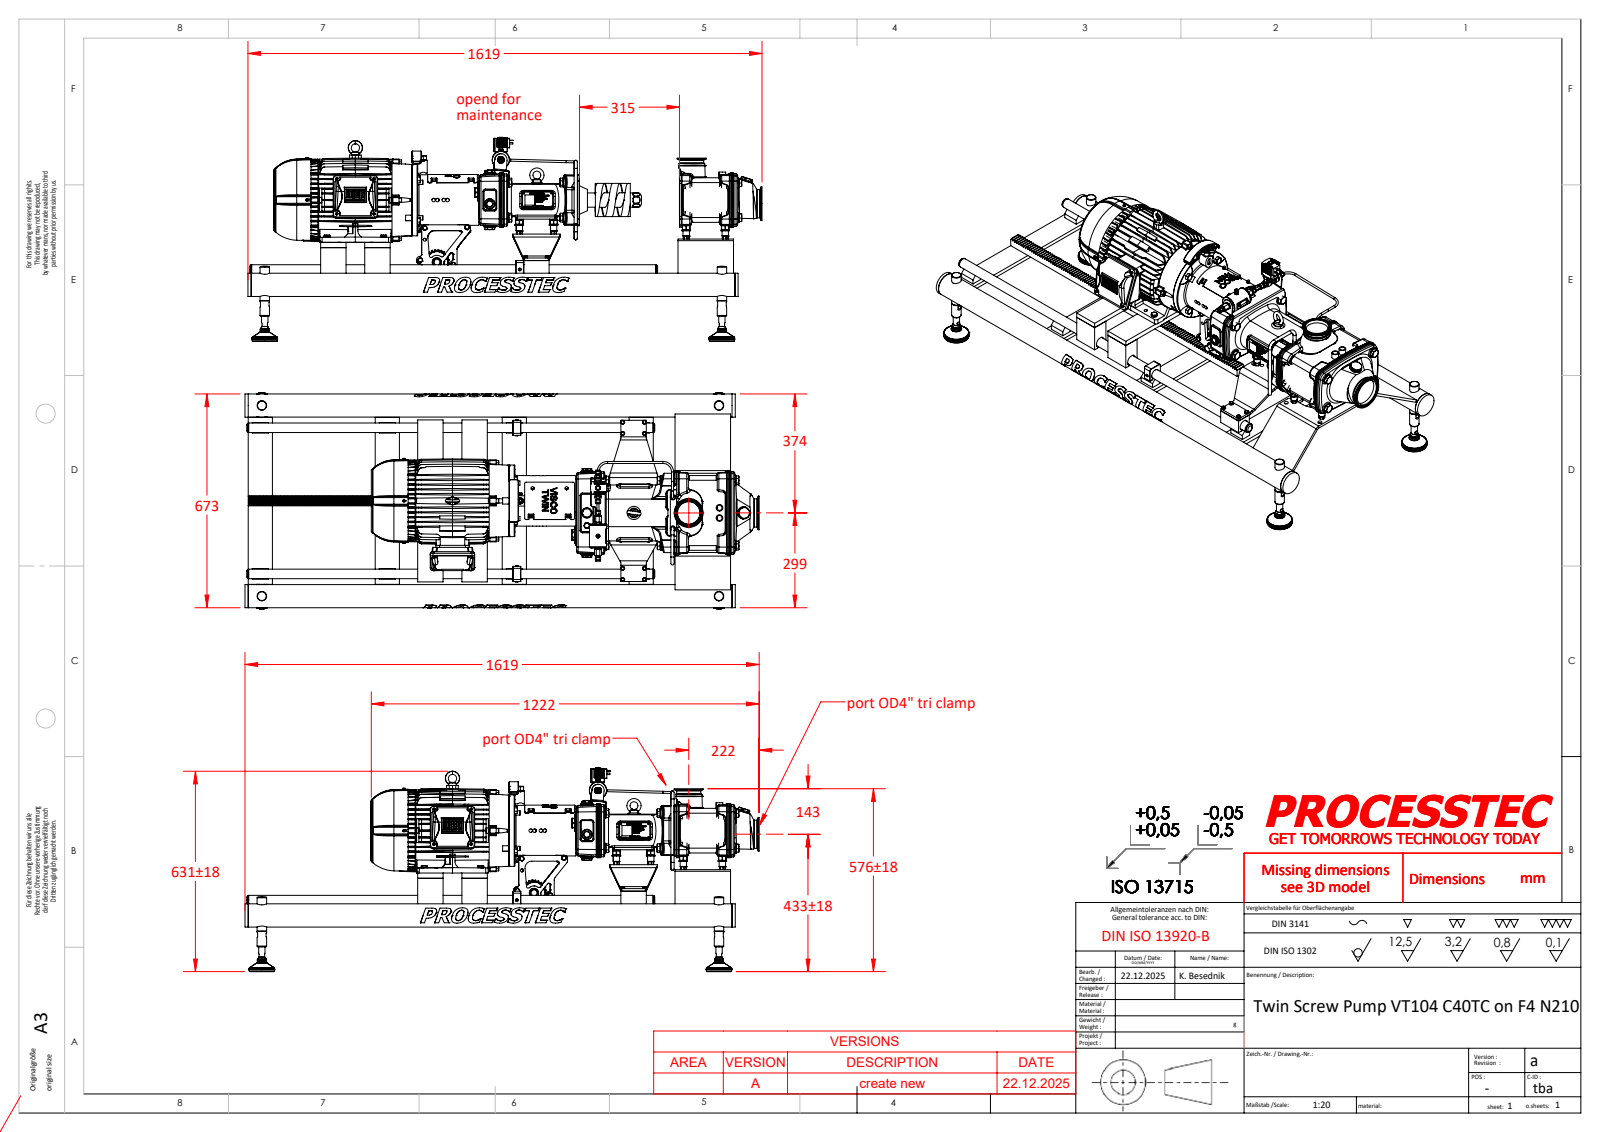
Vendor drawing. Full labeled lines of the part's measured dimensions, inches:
Part name (STEP PRODUCT): 001482; 001076; 001406; 000369 (+8 more)
STEP written by: SolidWorks 2023 (AUTOMOTIVE_DESIGN)
Units: inches
Bodies: 195 solids, 20316 faces (8834 planar, 4079 cylindrical, 7403 other)
Overall size (bounding box): 63.76 × 26.791 × 25.257
Volume: 3 233 in³ · Surface area: 10 180 in²
Round holes (diameter × count): ⌀0.335 ×22, ⌀0.197 ×21, ⌀0.315 ×13, ⌀0.433 ×12, ⌀0.512 ×12, ⌀0.268 ×11, ⌀0.252 ×10, ⌀0.413 ×9, ⌀0.689 ×9, ⌀0.398 ×8, ⌀0.402 ×8, ⌀0.404 ×8
Round bosses / shafts (diameter × count): ⌀0.394 ×38, ⌀0.236 ×22, ⌀0.945 ×20, ⌀0.669 ×16, ⌀0.787 ×12, ⌀0.591 ×10, ⌀0.472 ×9, ⌀1.063 ×8
Partial cylindrical surfaces — rounded edges, fillets, slot ends (radius × count): R0.039 ×1168, R0.059 ×113, R0.197 ×93, R0.019 ×50, R0.079 ×50, R0.236 ×50, R0.315 ×38, R0.118 ×35
Main face-to-face distances: 0.5, 0.315, 0.591, 1.181, 5.512, 4.866, 4.366, 5.012, 0.646, 0.217
Hole centre spacings: 18.166, 15.748, 9.055, 32.772, 2.165, 5.127, 24, 31.496
